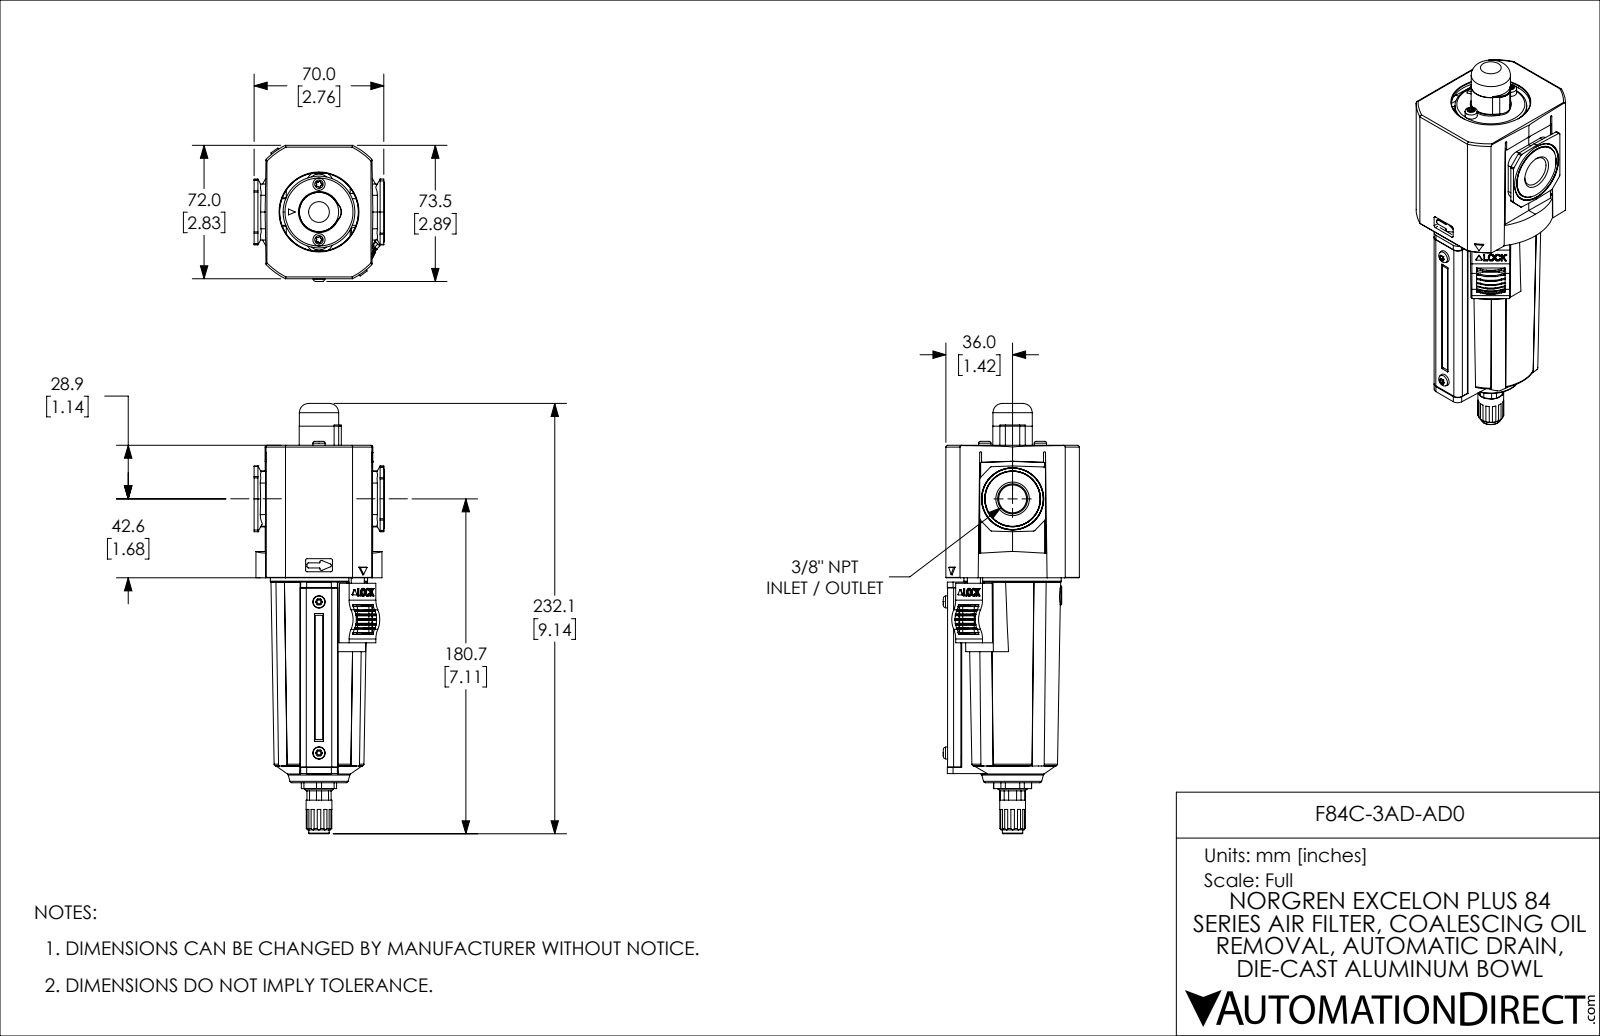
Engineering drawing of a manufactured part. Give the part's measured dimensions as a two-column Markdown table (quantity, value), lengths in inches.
| quantity | value |
| --- | --- |
| part name | F84C-3AD-AD0 |
| STEP written by | SolidWorks 2021 (CONFIG_CONTROL_DESIGN) |
| units | inches |
| bodies | 8 solids, 1363 faces (594 planar, 515 cylindrical, 254 other) |
| overall size | 9.139 × 2.892 × 2.766 |
| volume | 29.82 in³ |
| surface area | 174 in² |
| round holes (diameter × count) | 0.112 × 2, 0.163 × 2, 0.177 × 2, 0.22 × 1, 0.246 × 1, 0.633 × 1, 0.776 × 1, 2.461 × 1 |
| round bosses / shafts (diameter × count) | 0.315 × 2, 0.276 × 2, 0.26 × 2, 0.213 × 2, 2.122 × 1, 2.067 × 1, 2.018 × 1, 1.959 × 1 |
| partial cylindrical surfaces (radius × count) | 0.039 × 58, 0.02 × 57, 0.028 × 28, 0.01 × 18, 0.008 × 8, 0.038 × 8, 0.045 × 8, 0.06 × 8 |
| main face-to-face distances | 0.378, 2.457, 2.835, 2.047, 2.411, 2.756, 1.951, 0.461, 0.059, 0.364 |
| hole center spacings | 0.591, 0.594, 1.185, 1.181, 1.189, 2.504 |
